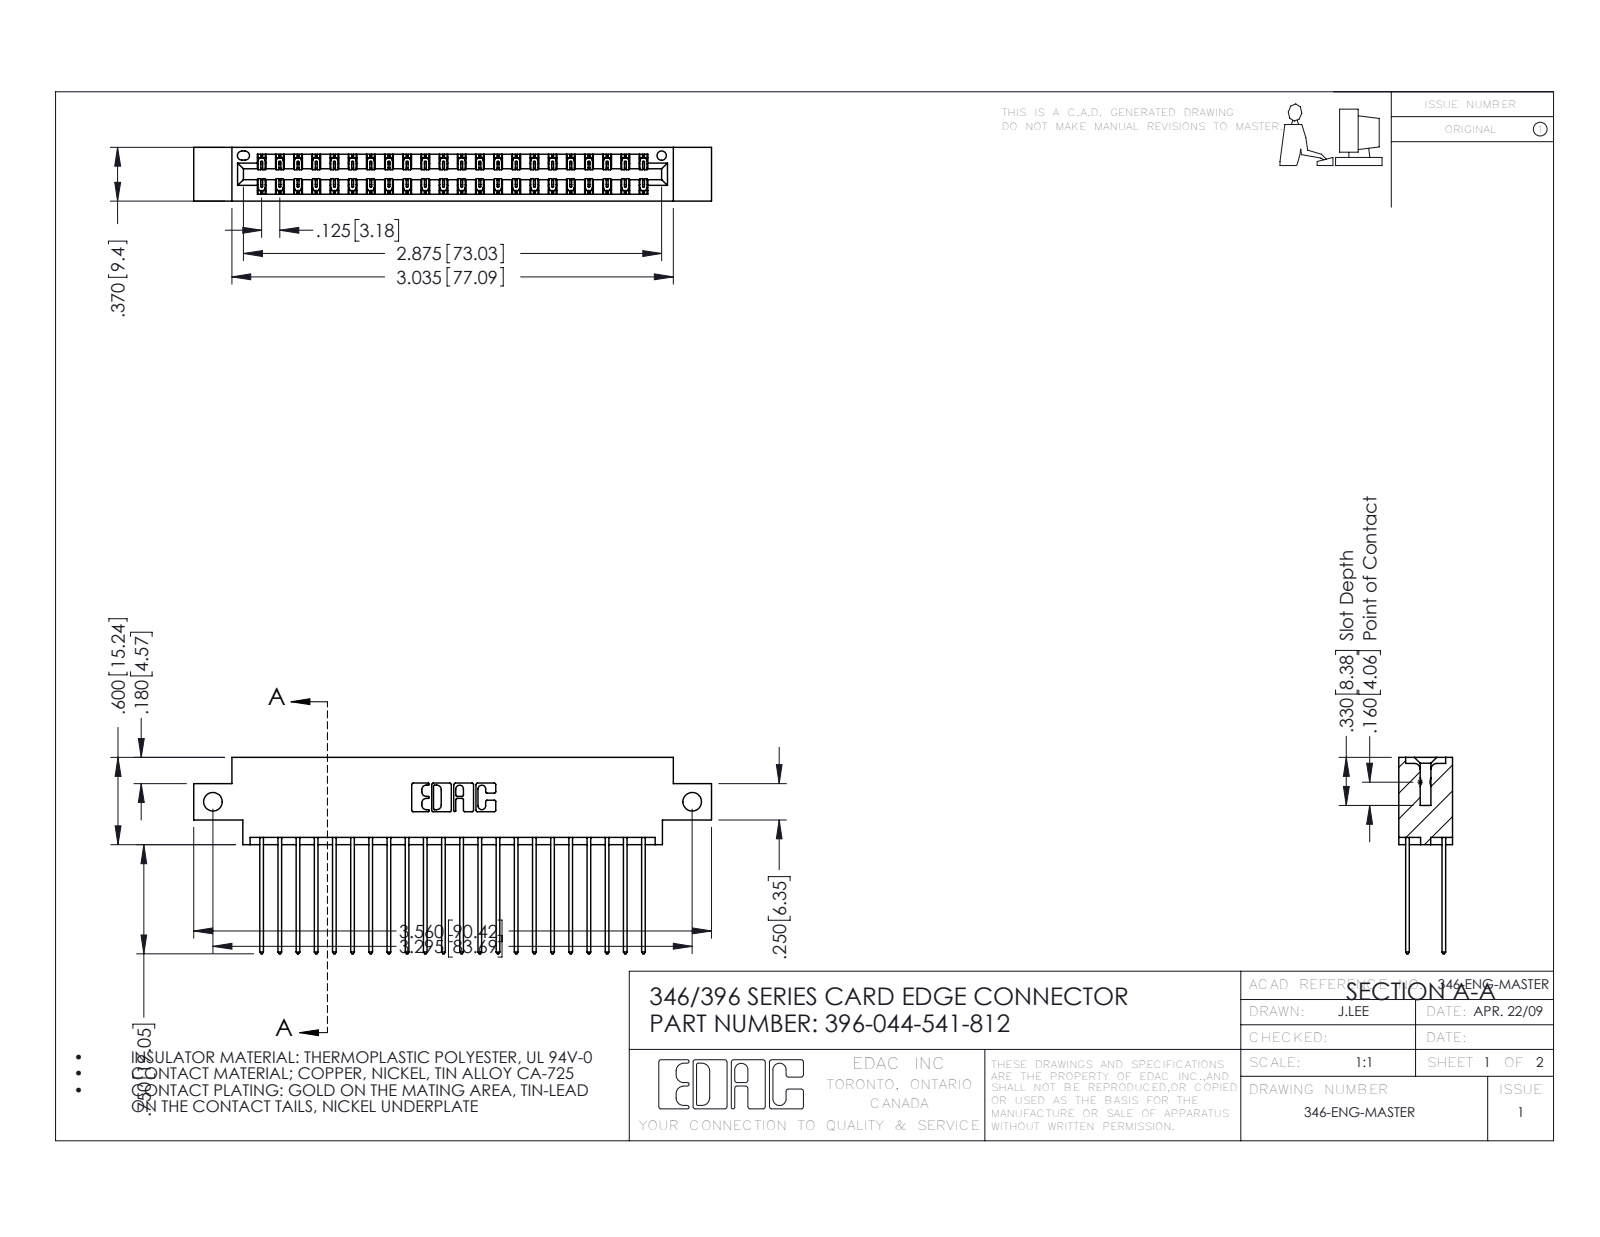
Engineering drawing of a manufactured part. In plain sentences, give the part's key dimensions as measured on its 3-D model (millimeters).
The part is named "346 Part_0.170 Offset - Side Mount; 396-044-541-812; 345-292-001_345-293-141". Its 3-D file was written by "SolidWorks 2016 (CONFIG_CONTROL_DESIGN)". It is 45 solids with 2414 faces: 1620 planar, 794 cylindrical and 0 other. Overall it measures 90.4 by 34.3 by 9.4 millimeters. Its volume is 8 670 cubic millimeters and its surface area 12 860 square millimeters. Round holes: 2 of diameter 3.3, 1 of diameter 1.6. Partial cylindrical surfaces (rounded edges, fillets, slot ends): 66 of radius 0.2, 44 of radius 0.3, 22 of radius 0.3, 6 of radius 0.2, 6 of radius 0.8, 3 of radius 0.7, 2 of radius 0.4, 2 of radius 0.6. The main face-to-face distances are 1.2, 8.2, 6.4, 1.8, 7.6, 0.6, 9.4, 7, 5.7, 3.8. The hole center spacings are 83.7.
